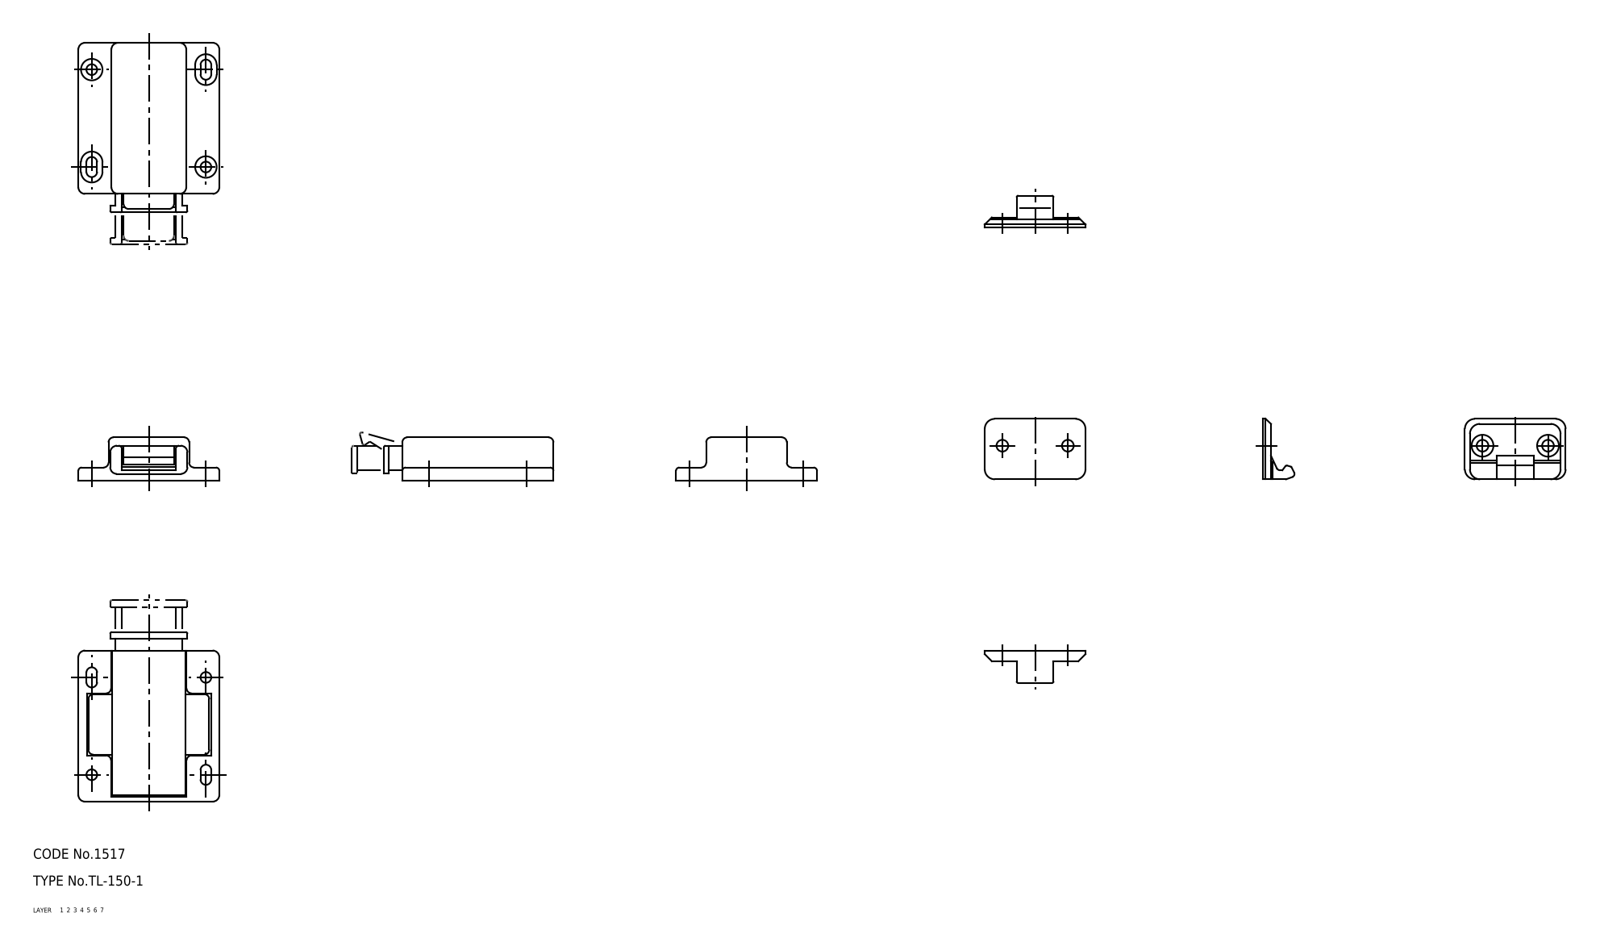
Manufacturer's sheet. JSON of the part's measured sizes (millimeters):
{"part_name": "housing_A; arm; housing_B; n_holder (+2 more)", "step_written_by": "SolidWorks 2015 (AUTOMOTIVE_DESIGN)", "units": "millimeters", "bodies": {"solids": 5, "faces": 217, "planar": 99, "cylindrical": 82, "other": 36}, "overall_size": [53.5, 42, 22], "volume_mm3": 13243, "surface_area_mm2": 13024, "round_holes": [[3.2, 2], [3.5, 2], [6.4, 2]], "partial_cylinders_radius": [[1.5, 14], [2, 14], [1, 10], [3, 8], [0.1, 7], [0.5, 4], [1.6, 4], [3.2, 4]], "face_to_face_distances": [3.2, 2.5, 13, 10.5, 2, 9, 4, 7.3, 6.5, 9.8], "hole_center_spacings": [19.5, 44.69]}
